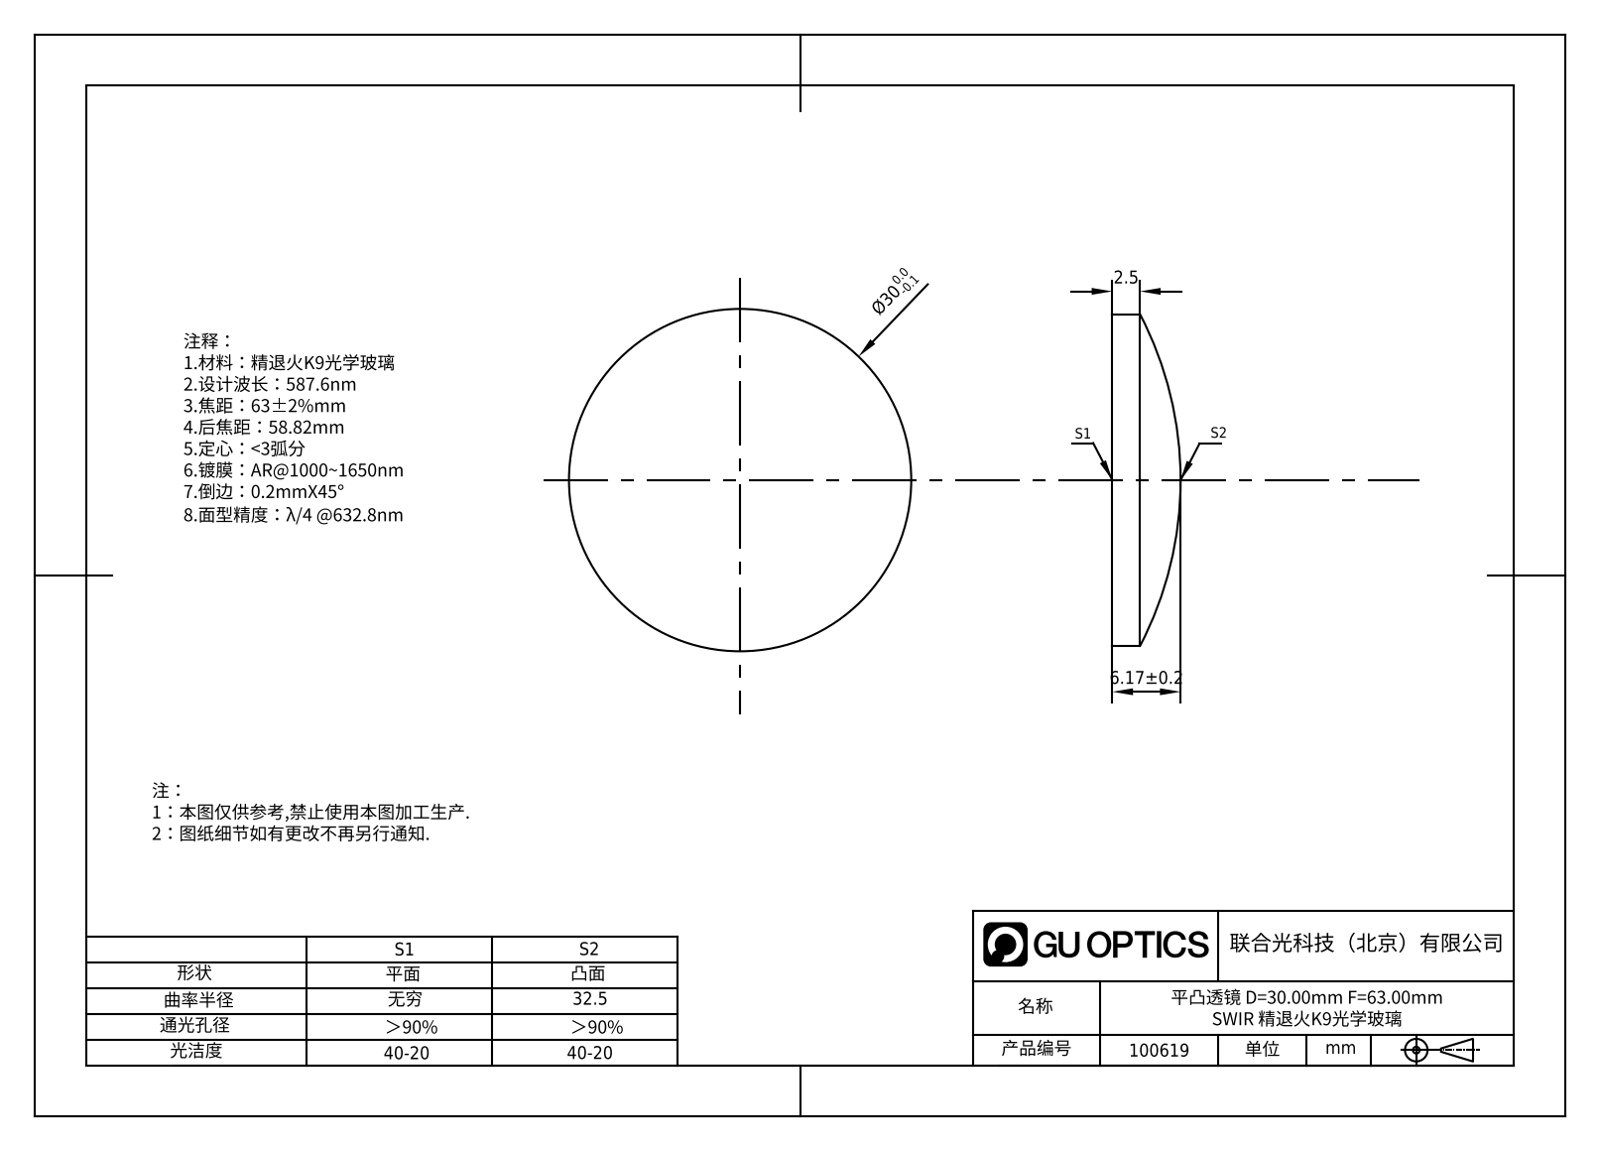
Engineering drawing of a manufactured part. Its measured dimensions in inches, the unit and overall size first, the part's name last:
Units: inches
Overall size (bounding box): 1.181 × 1.181 × 0.243
Round bosses / shafts (diameter × count): ⌀1.181 ×1
Volume: 0.189 in³ · Surface area: 2.623 in²
Bodies: 1 solid, 5 faces (1 planar, 2 cylindrical, 2 other)
Part name (STEP PRODUCT): 100596
STEP written by: SolidWorks 2020 (CONFIG_CONTROL_DESIGN)
